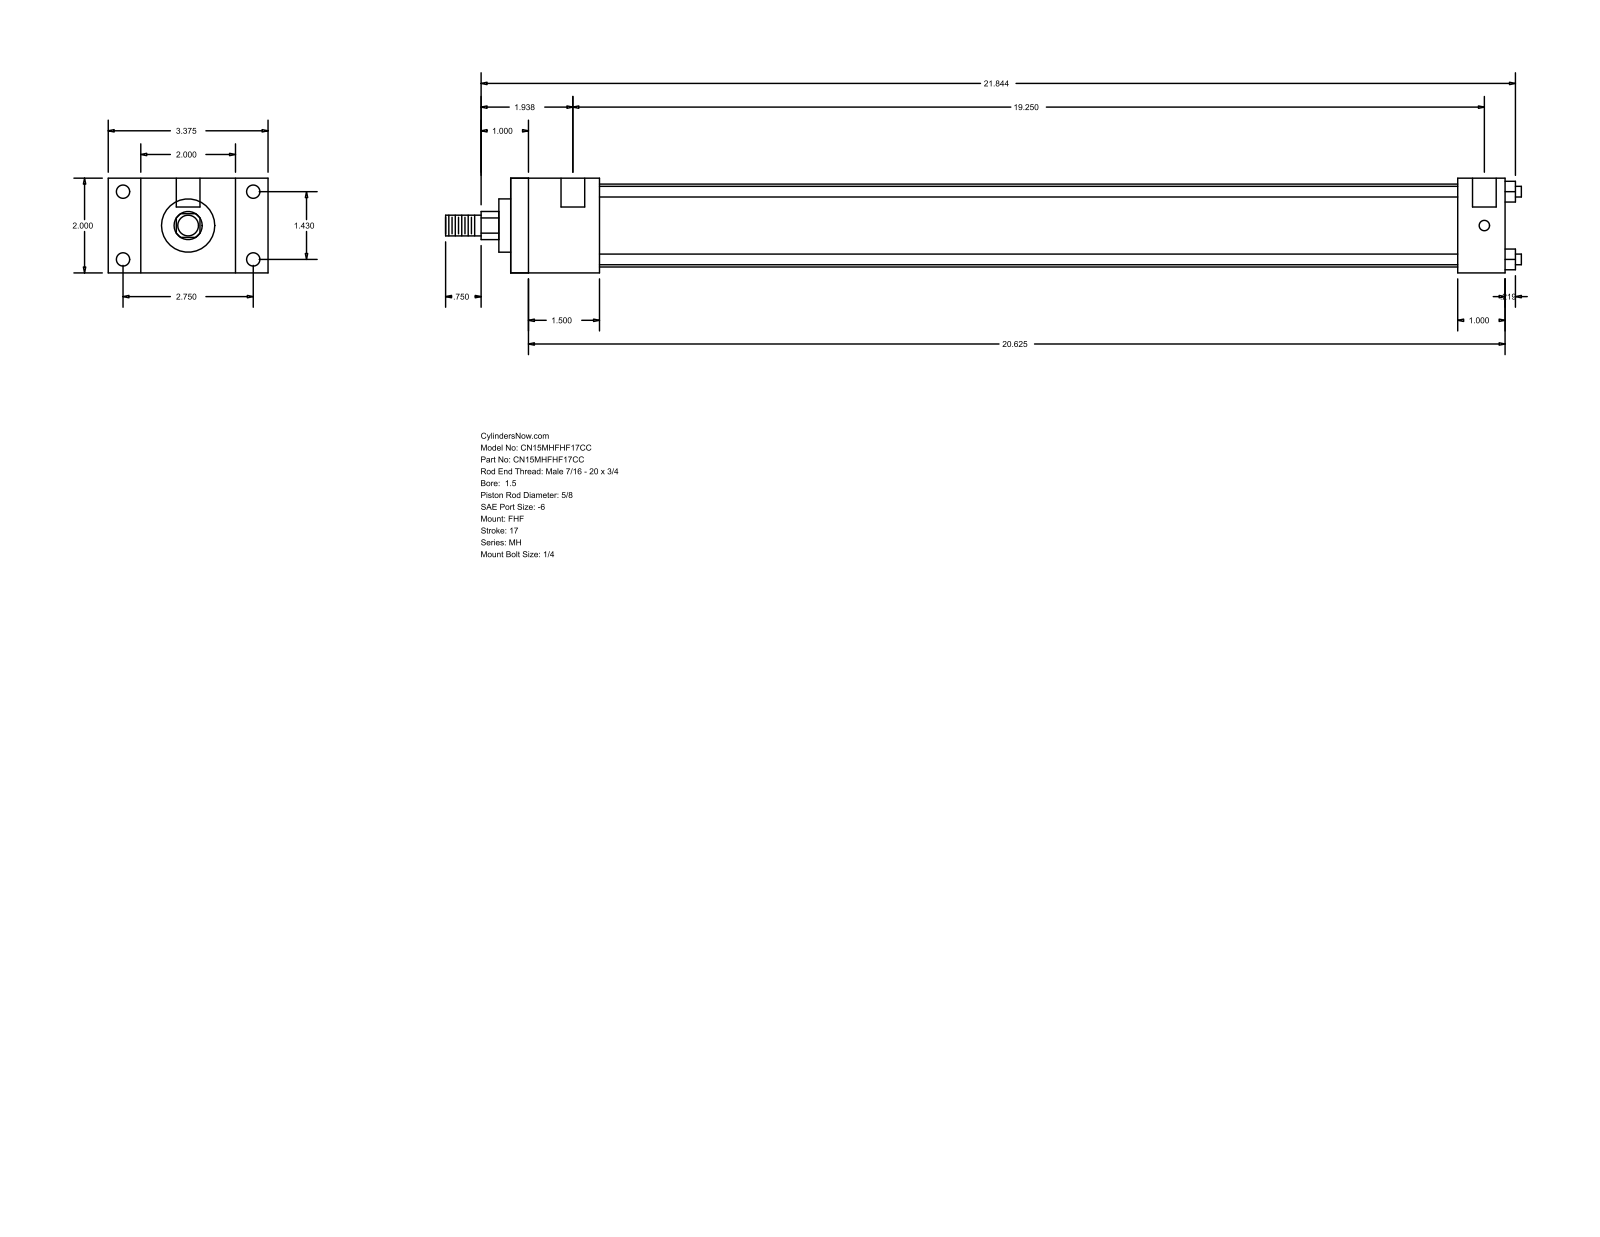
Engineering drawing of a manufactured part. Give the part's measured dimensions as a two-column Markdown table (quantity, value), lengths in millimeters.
| quantity | value |
| --- | --- |
| part name | MH_FHF__0150_0.625 |
| STEP written by | GSSL Pune (CONFIG_CONTROL_DESIGN) |
| units | millimeters |
| bodies | 0 solids, 88 faces (60 planar, 28 cylindrical, 0 other) |
| overall size | 577.06 × 85.72 × 50.8 |
| round holes (diameter × count) | 5.56 × 4, 7.14 × 4, 12.7 × 2 |
| round bosses / shafts (diameter × count) | 5.71 × 4, 44.45 × 1, 28.57 × 1, 15.88 × 1, 11.11 × 1 |
| partial cylindrical surfaces (radius × count) | 7.54 × 1 |
| main face-to-face distances | 50.8, 17.46, 68.26, 47.62, 85.72, 533.39, 485.77, 508, 460.38, 25.39 |
| hole center spacings | 36.32, 69.84, 78.72, 492.12, 3.17, 488.95 |
